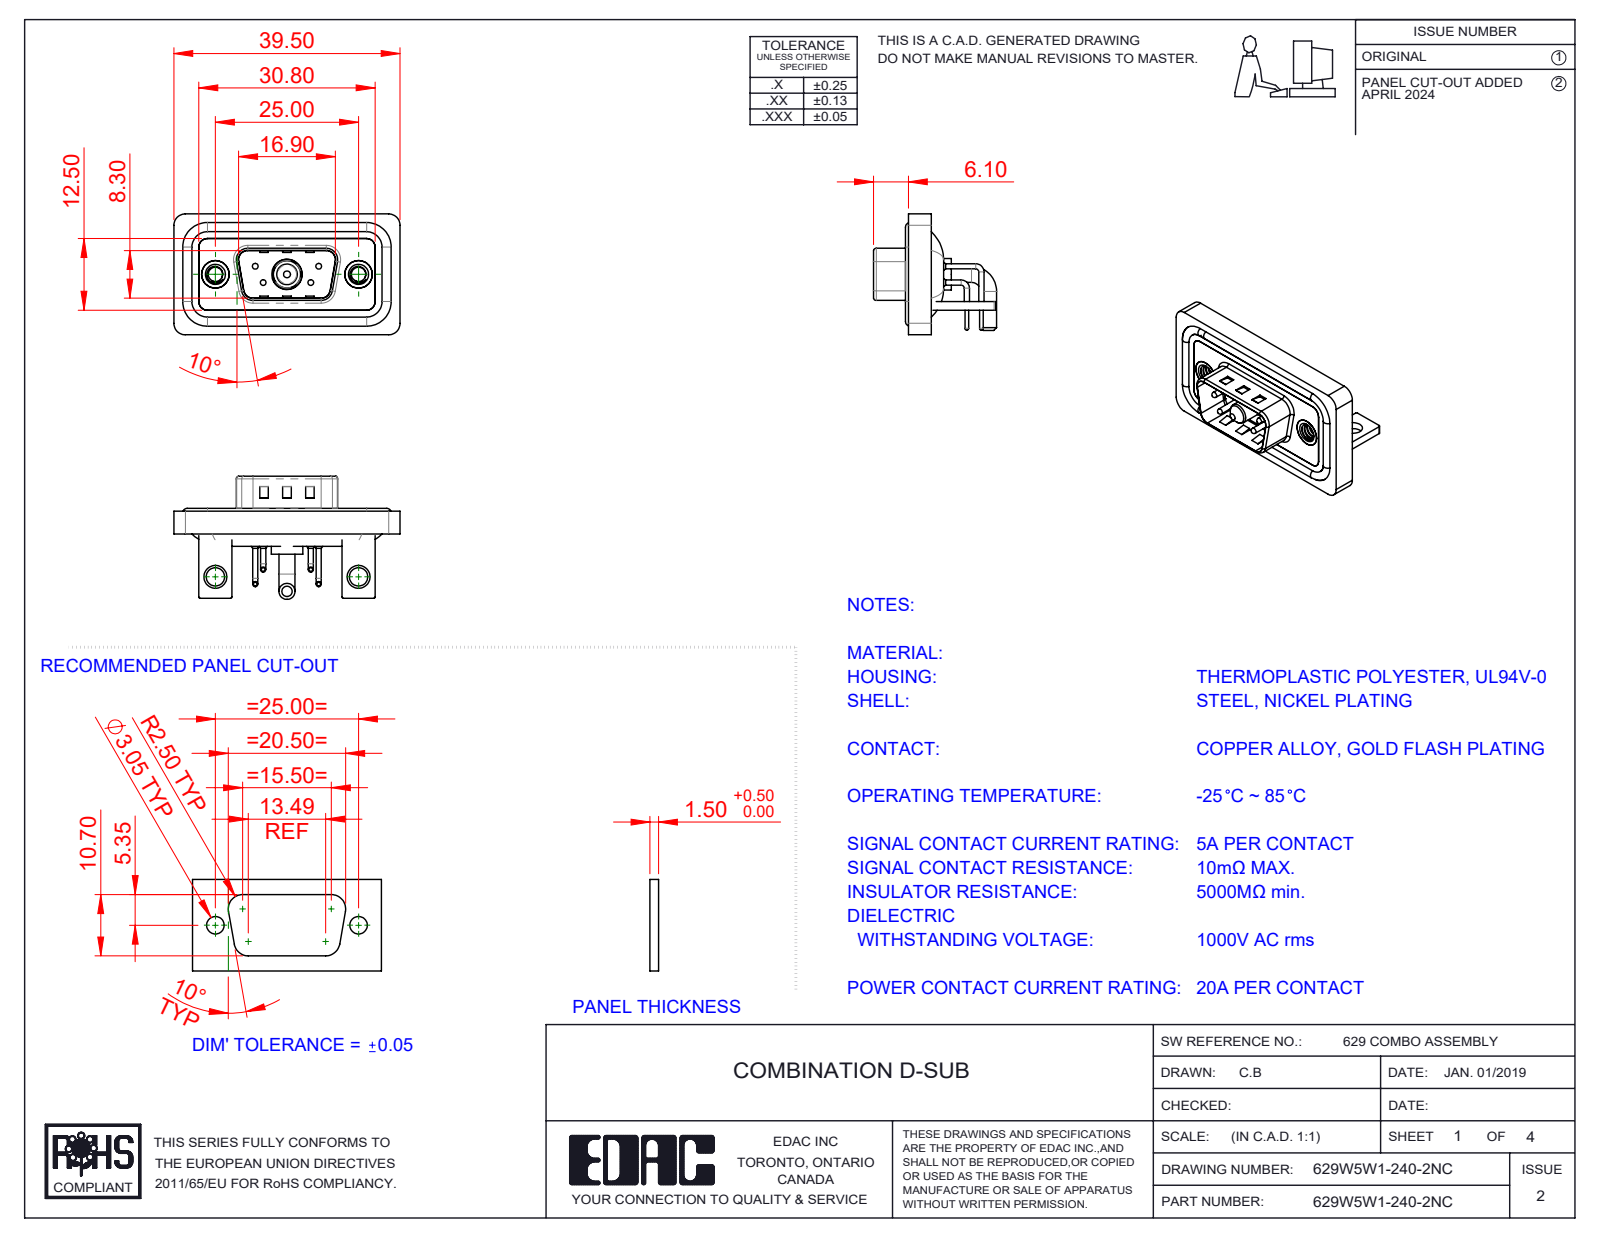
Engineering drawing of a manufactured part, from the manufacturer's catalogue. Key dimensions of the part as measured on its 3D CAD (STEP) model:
Part name (STEP PRODUCT): 629Combo Stabilizer Bracket; 629Combo Shell Rear_09 Contacts; 629Combo Housing_5W1; 629Combo Contact Row 1 (+6 more)
STEP written by: SolidWorks 2023 (CONFIG_CONTROL_DESIGN)
Units: millimetres
Bodies: 15 solids, 932 faces (431 planar, 363 cylindrical, 138 other)
Overall size (bounding box): 39.5 × 21.5 × 21.1
Volume: 4 748 mm³ · Surface area: 7 752 mm²
Round holes (diameter × count): ⌀0.75 ×4, ⌀1.6 ×4, ⌀2 ×4, ⌀2.5 ×2, ⌀3.2 ×2, ⌀4 ×2, ⌀4.8 ×2, ⌀5 ×2, ⌀4.85 ×1, ⌀5.3 ×1
Round bosses / shafts (diameter × count): ⌀0.9 ×8, ⌀1.6 ×4, ⌀1.5 ×4, ⌀1 ×4, ⌀0.65 ×4, ⌀4.9 ×2, ⌀2.8 ×2, ⌀5.5 ×1
Partial cylindrical surfaces — rounded edges, fillets, slot ends (radius × count): R2 ×19, R1.5 ×18, R0.25 ×16, R0.5 ×9, R1.6 ×8, R0.6 ×4, R0.65 ×4, R0.9 ×4
Main face-to-face distances: 0.4, 1.5, 0.8, 2.9, 1.1, 2.1, 1.2, 1.6, 2.5, 3.7
Hole centre spacings: 3.16, 5.72, 7.1, 12.5, 18.1, 25, 4.39, 4.4
